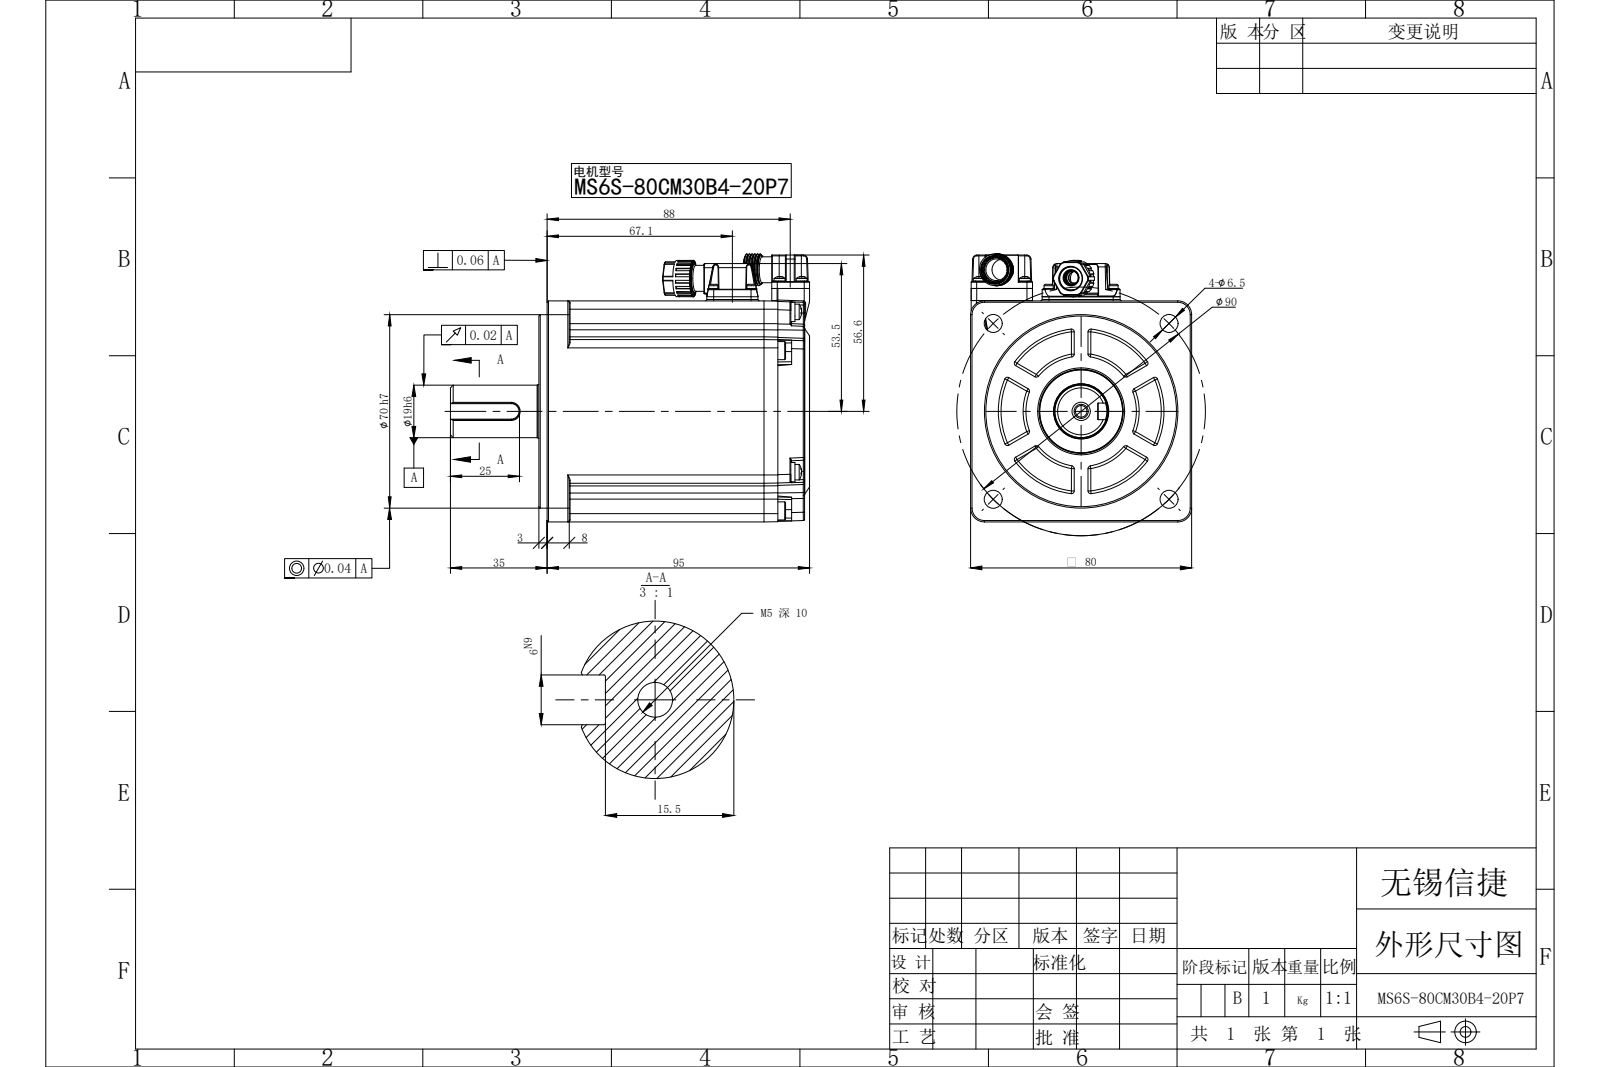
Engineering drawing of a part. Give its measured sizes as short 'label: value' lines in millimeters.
name: MS6S-80CM30B4-20P7
written by: SolidWorks 2022 (CONFIG_CONTROL_DESIGN)
unit: mm
bodies: 0 solids, 1376 faces (495 planar, 477 cylindrical, 404 other)
size: 130 × 97.85 × 80
holes: 4× ⌀6.5, 2× ⌀11.7, 1× ⌀4.2, 1× ⌀5, 1× ⌀5.5, 1× ⌀10.4, 1× ⌀11.5, 1× ⌀20
bosses: 4× ⌀7, 4× ⌀6.53, 4× ⌀5.6, 4× ⌀4, 4× ⌀3.9, 4× ⌀3.3, 2× ⌀9.4, 1× ⌀70
rounds: 50× R0.5, 47× R0.3, 39× R1, 29× R3, 20× R0.2, 13× R0.35, 13× R1.5, 8× R2
face distances: 80, 14, 66, 95, 9.7, 1.8, 93.2, 83.5, 11.5, 3
hole spacings: 45, 63.64, 90, 33.18, 33.2, 33.26, 33.27
